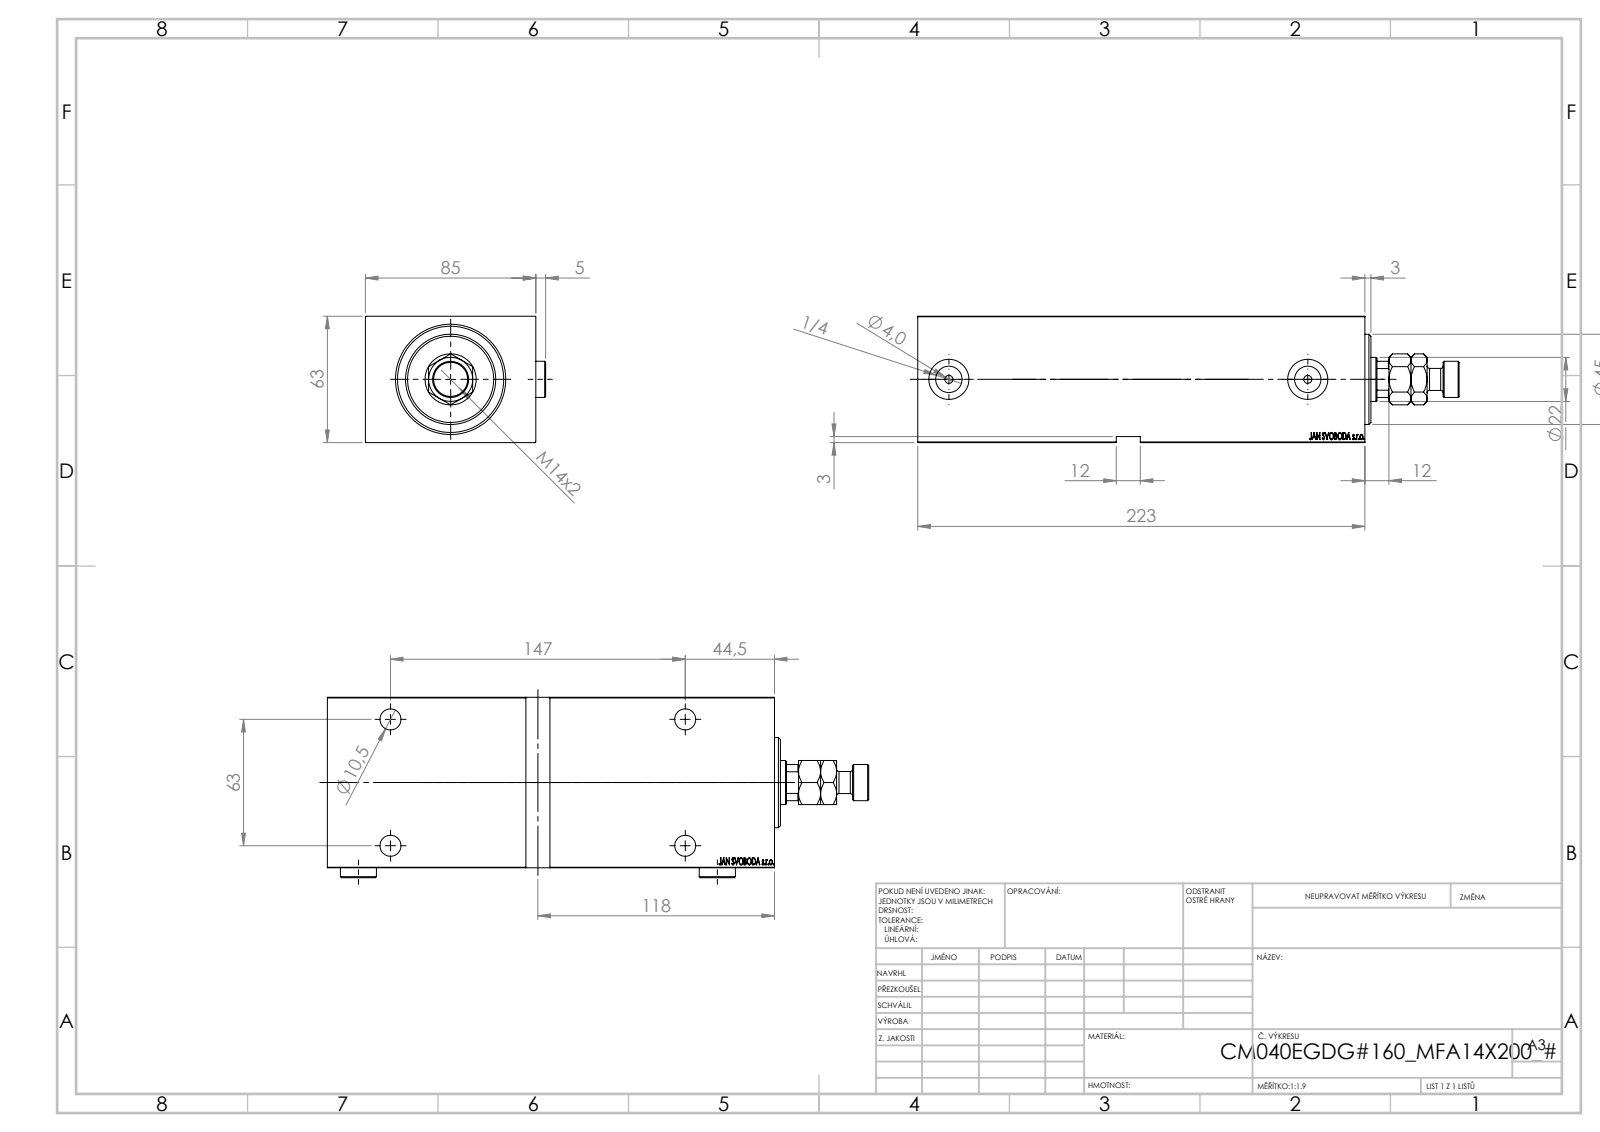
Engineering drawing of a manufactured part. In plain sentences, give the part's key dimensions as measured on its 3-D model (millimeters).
The part is named "V450CM_E_Body; MFA; Zatka_OIL_PORT; V450CM_E_VCP (+1 more)". Its 3-D file was written by "SolidWorks 2019 (CONFIG_CONTROL_DESIGN)". It is 6 solids with 964 faces: 462 planar, 72 cylindrical and 430 other. Overall it measures 270 by 89.9 by 63 millimeters. Its volume is 1 036 000 cubic millimeters and its surface area 148 688 square millimeters. Round holes: 4 of diameter 10.5, 4 of diameter 16.5, 2 of diameter 4, 2 of diameter 13.16, 2 of diameter 20, 1 of diameter 12.5, 1 of diameter 22, 1 of diameter 25.5, 1 of diameter 40, 1 of diameter 53. Round bosses or shafts: 3 of diameter 18, 1 of diameter 45, 1 of diameter 42, 1 of diameter 11. Partial cylindrical surfaces (rounded edges, fillets, slot ends): 1 of radius 10.5. The main face-to-face distances are 63, 85, 223, 12, 211, 5, 3, 206, 218, 60. The hole center spacings are 63, 147, 159.93, 179.
